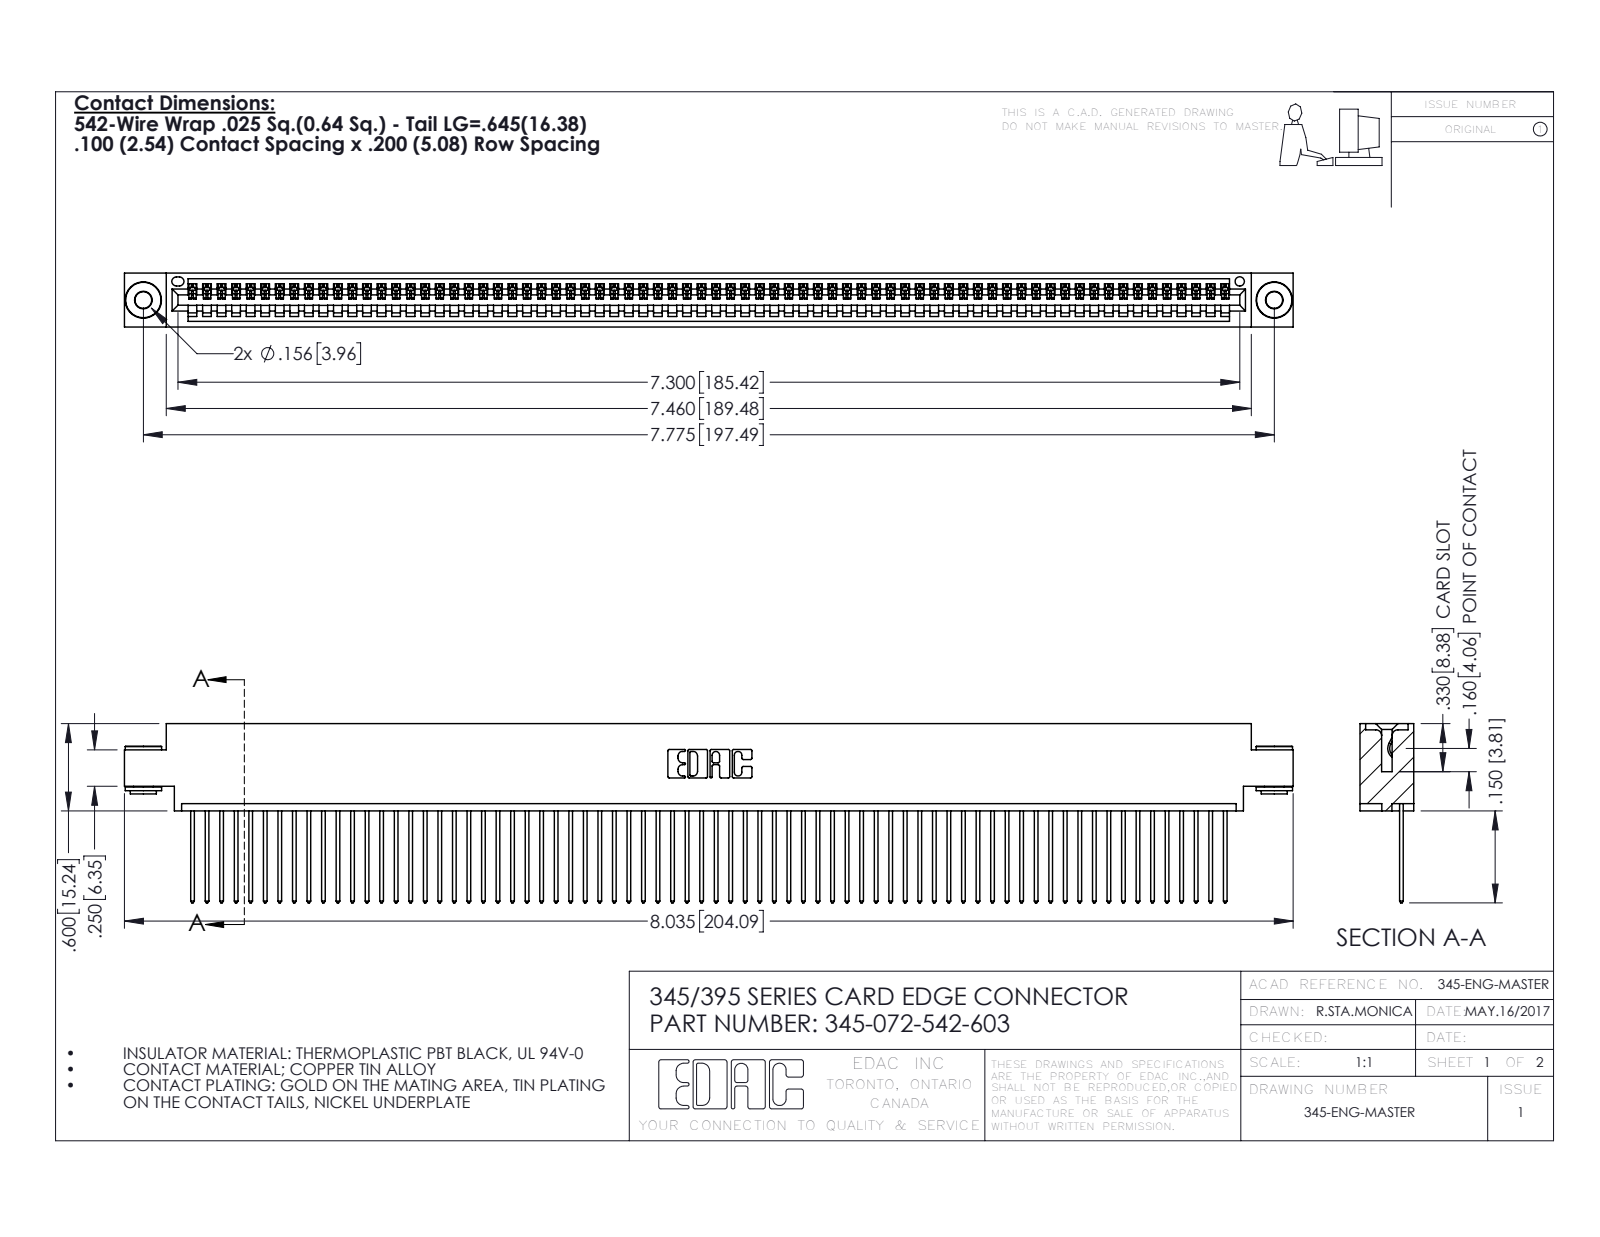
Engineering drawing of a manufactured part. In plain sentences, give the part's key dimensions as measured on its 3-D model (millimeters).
The part is named "345 Part_0.170 Offset - 0.156 Dia-TH; 345-250-002_345-250-002-102; 345-072-542-603; 345-292-001_345-293-142". Its 3-D file was written by "SolidWorks 2016 (CONFIG_CONTROL_DESIGN)". It is 75 solids with 4344 faces: 2974 planar, 1362 cylindrical and 8 other. Overall it measures 204.1 by 31.3 by 9.4 millimeters. Its volume is 19 700 cubic millimeters and its surface area 27 940 square millimeters. Round holes: 2 of diameter 2.9, 2 of diameter 4, 1 of diameter 1.6. Round bosses or shafts: 2 of diameter 6.4, 2 of diameter 4.6, 2 of diameter 3.5. Partial cylindrical surfaces (rounded edges, fillets, slot ends): 144 of radius 0.2, 144 of radius 0.3, 22 of radius 0.3, 6 of radius 0.2, 6 of radius 0.8, 3 of radius 0.7, 2 of radius 0.8, 2 of radius 1. The main face-to-face distances are 1.8, 7.6, 9.4, 2.5, 6.9, 0.6, 5.1, 5.7, 4.4, 3.8. The hole center spacings are 6.9, 191.5, 197.5.
